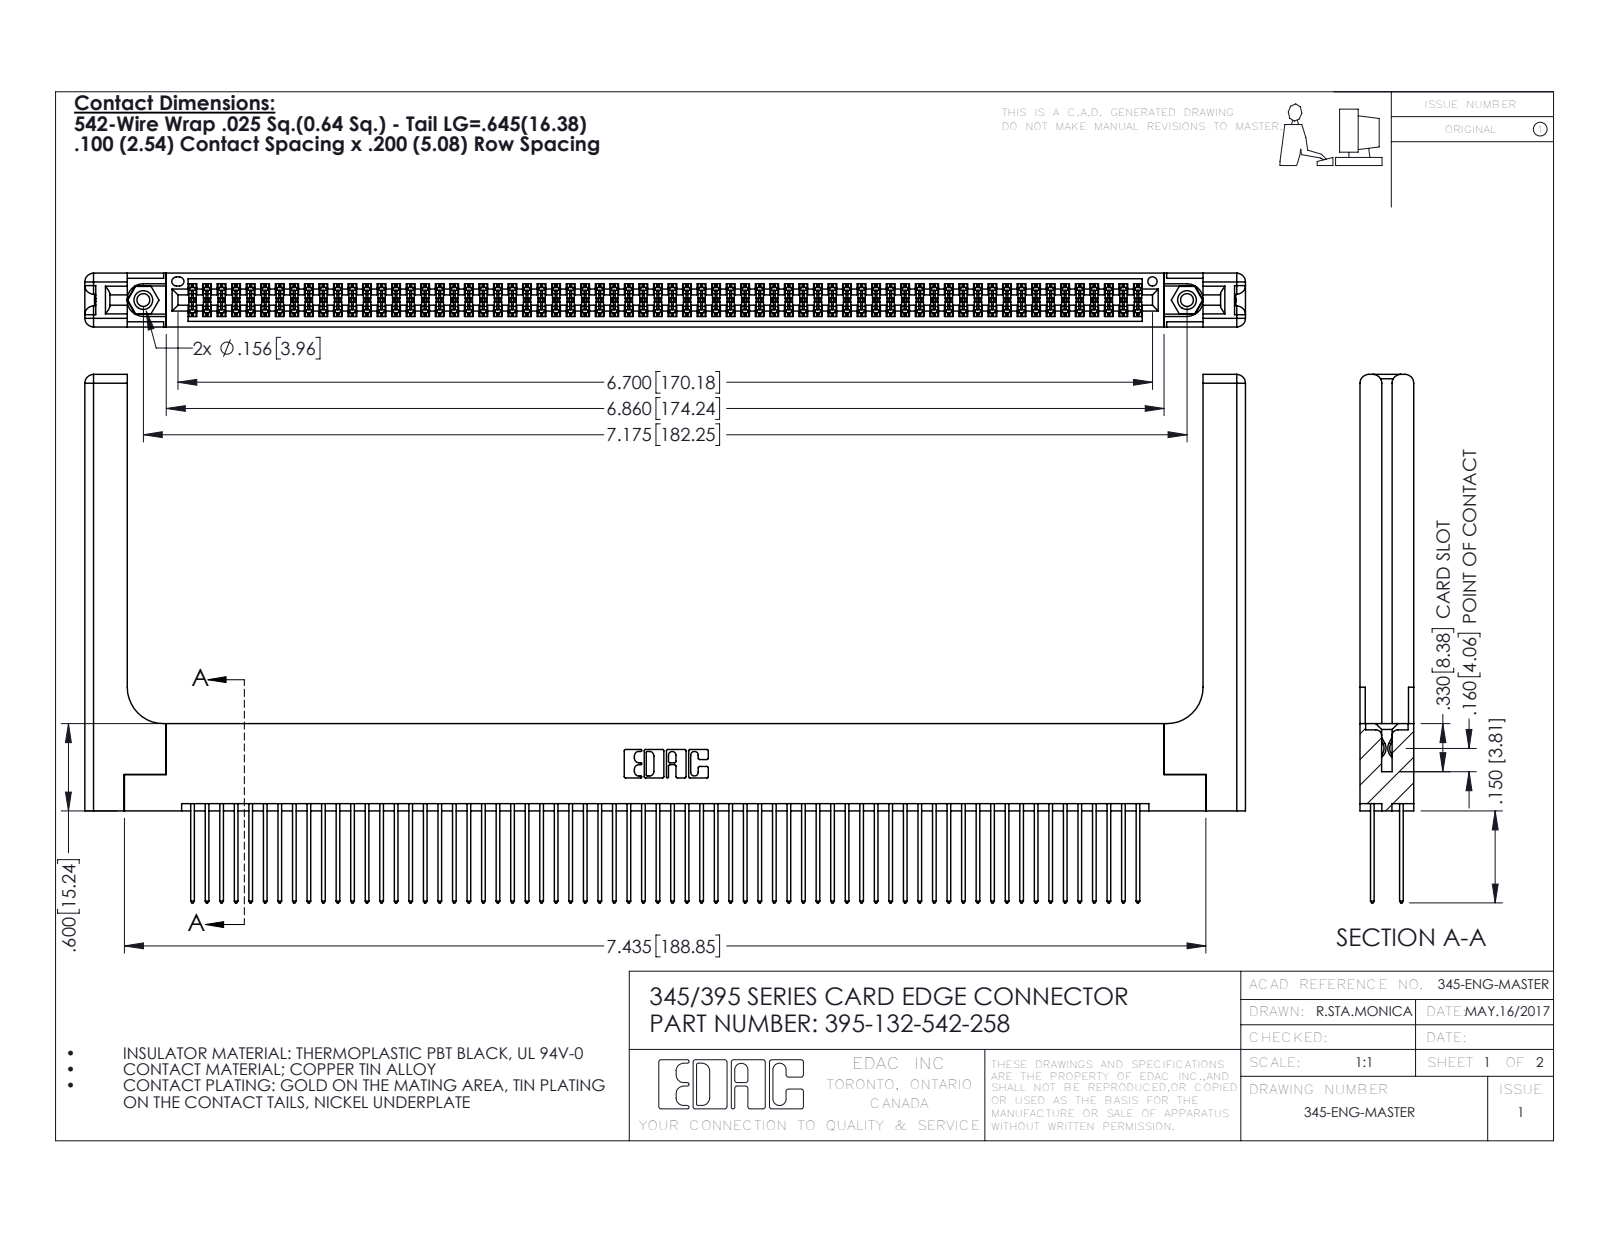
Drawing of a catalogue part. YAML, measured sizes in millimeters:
part_name: "345-250-001_345-250-001-102; 345-220-058_345-220-058; 345-292-001_345-293-142; 345 Part_Flush Mounting Lugs - 0.156 Dia-TH (+1 more)"
step_written_by: "SolidWorks 2016 (CONFIG_CONTROL_DESIGN)"
units: millimeters
bodies: {solids: 137, faces: 6982, planar: 4584, cylindrical: 2338, other: 60}
overall_size: [202.7, 92.3, 9.4]
volume: 29010
surface_area: 38740
round_holes:
  - {diameter: 2.3, count: 2}
  - {diameter: 3.2, count: 2}
  - {diameter: 4, count: 2}
  - {diameter: 1.6, count: 1}
round_bosses_or_shafts:
  - {diameter: 3.9, count: 2}
partial_cylinders:
  - {radius: 0.2, count: 198}
  - {radius: 0.3, count: 132}
  - {radius: 0.3, count: 22}
  - {radius: 1.5, count: 16}
  - {radius: 0.2, count: 6}
  - {radius: 0.8, count: 6}
  - {radius: 0.7, count: 3}
  - {radius: 0.4, count: 2}
face_to_face_distances: [1.8, 7.6, 5.1, 2.5, 6.9, 0.6, 9.4, 5.7, 4.4, 3.8]
hole_center_spacings: [6.9, 176.3, 182.2]
